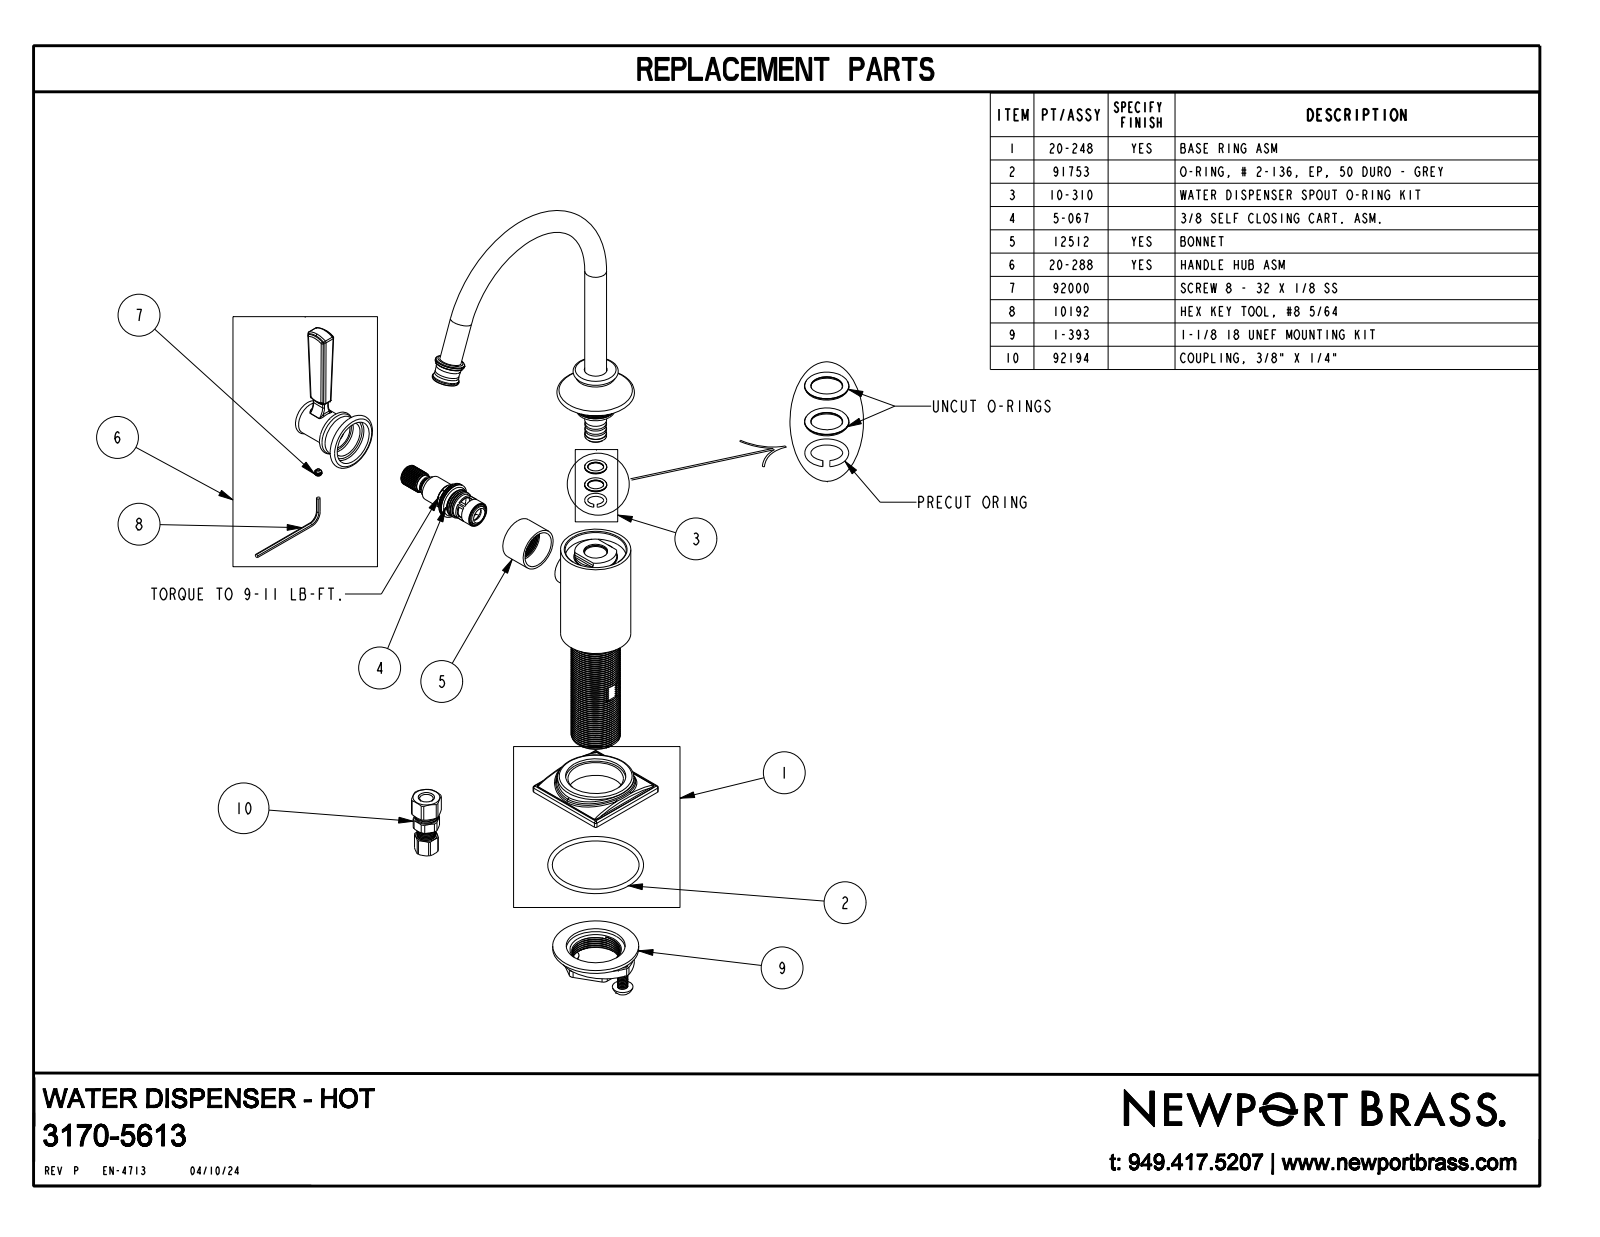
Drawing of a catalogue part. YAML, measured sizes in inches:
part_name: "3170-5613"
step_written_by: "CREO PARAMETRIC BY PTC INC, 2018400 (CONFIG_CONTROL_DESIGN)"
units: inches
bodies: {solids: 1, faces: 238, planar: 25, cylindrical: 57, other: 156}
overall_size: [9.497, 6.053, 3.585]
volume: 10.73
surface_area: 53.08
round_holes:
  - {diameter: 1, count: 1}
round_bosses_or_shafts:
  - {diameter: 0.5, count: 2}
  - {diameter: 1.75, count: 1}
  - {diameter: 1.61, count: 1}
  - {diameter: 0.97, count: 1}
  - {diameter: 0.76, count: 1}
partial_cylinders:
  - {radius: 0.04, count: 16}
  - {radius: 0.02, count: 10}
  - {radius: 0.03, count: 6}
  - {radius: 0.037, count: 4}
  - {radius: 0.33, count: 2}
  - {radius: 0.45, count: 1}
  - {radius: 0.57, count: 1}
face_to_face_distances: [3.47, 2.05, 1.49, 1.535, 3.585, 0.045, 2.095, 0.067, 1.982, 0.425]
